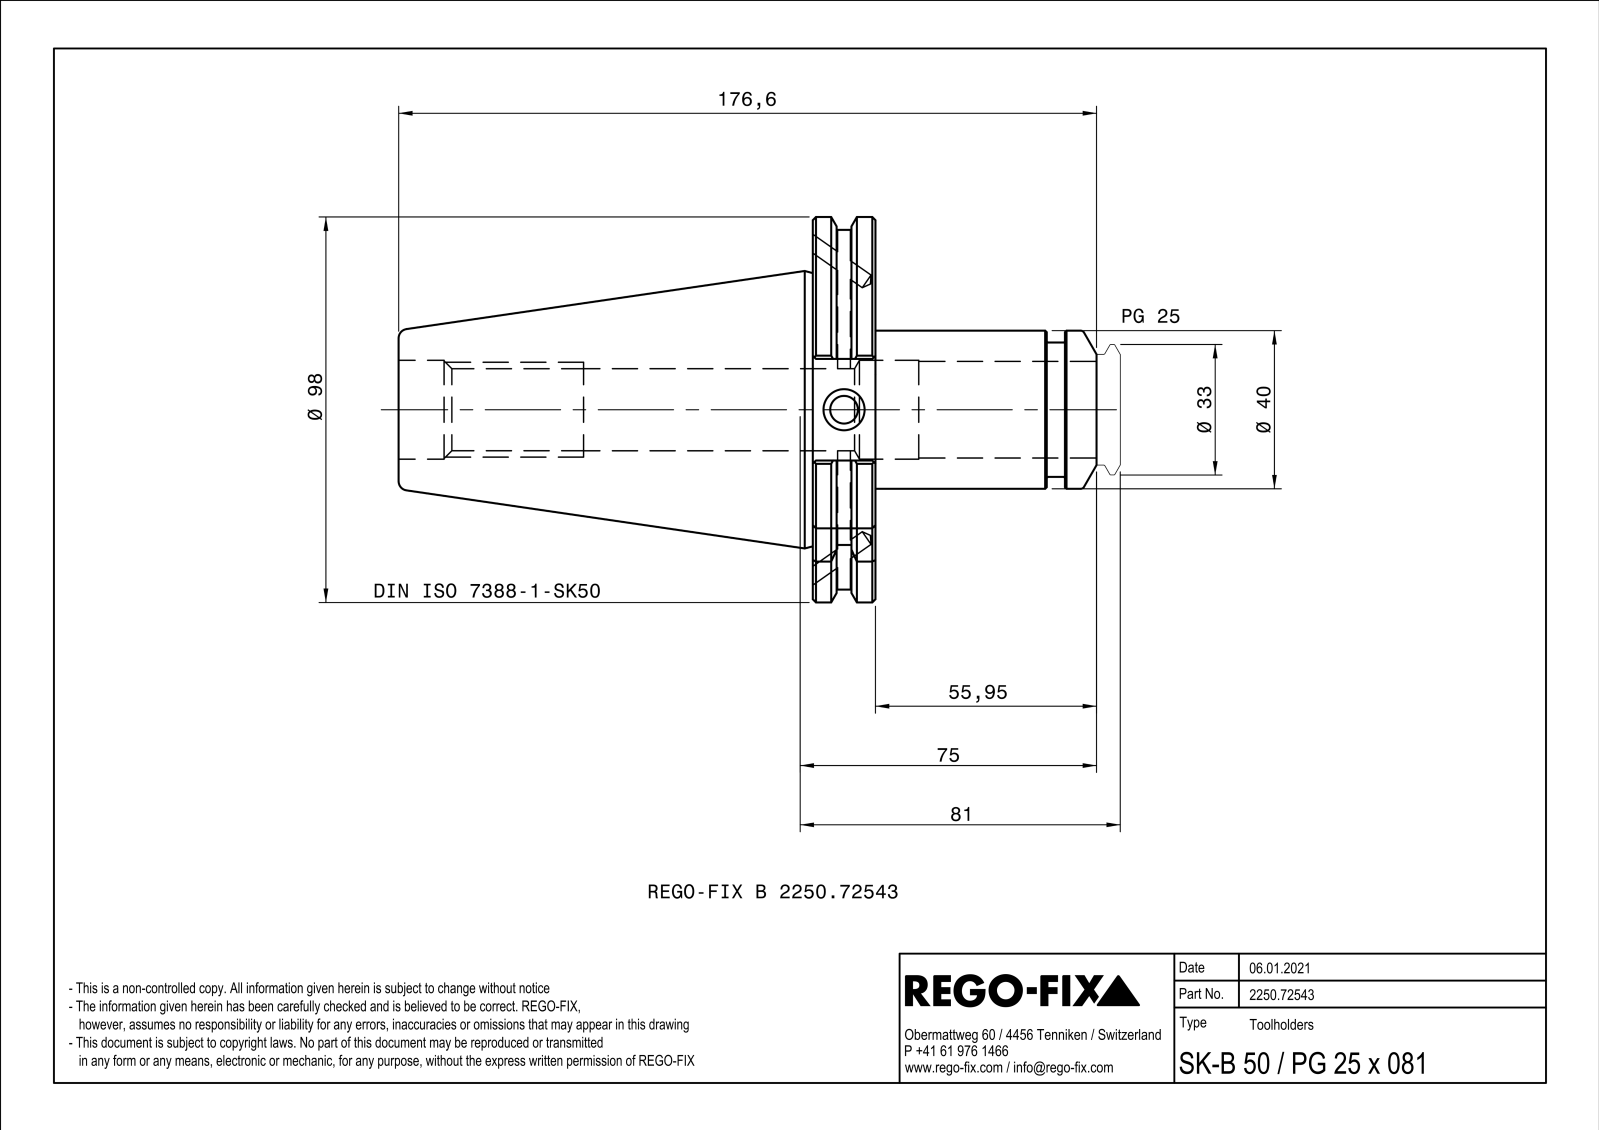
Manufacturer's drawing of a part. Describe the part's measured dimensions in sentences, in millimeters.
The part is named "NOCUT". Its 3-D file was written by "SIEMENS PLM Software Solid Edge ST10 (AUTOMOTIVE_DESIGN)". It is 1 solid with 120 faces: 43 planar, 33 cylindrical and 44 other. Overall it measures 176.6 by 97.5 by 93.58 millimeters. Its volume is 360 167 cubic millimeters and its surface area 54 972 square millimeters. Round holes: 5 of diameter 3.5, 1 of diameter 7, 1 of diameter 10, 1 of diameter 20.75, 1 of diameter 25. Round bosses or shafts: 1 of diameter 40, 1 of diameter 34. Partial cylindrical surfaces (rounded edges, fillets, slot ends): 5 of radius 0.5, 1 of radius 45.5, 1 of radius 48.75. The main face-to-face distances are 15.85, 120.65, 104.8, 72.8, 43.35, 59.2, 164, 4.6, 47.95, 63.8.
